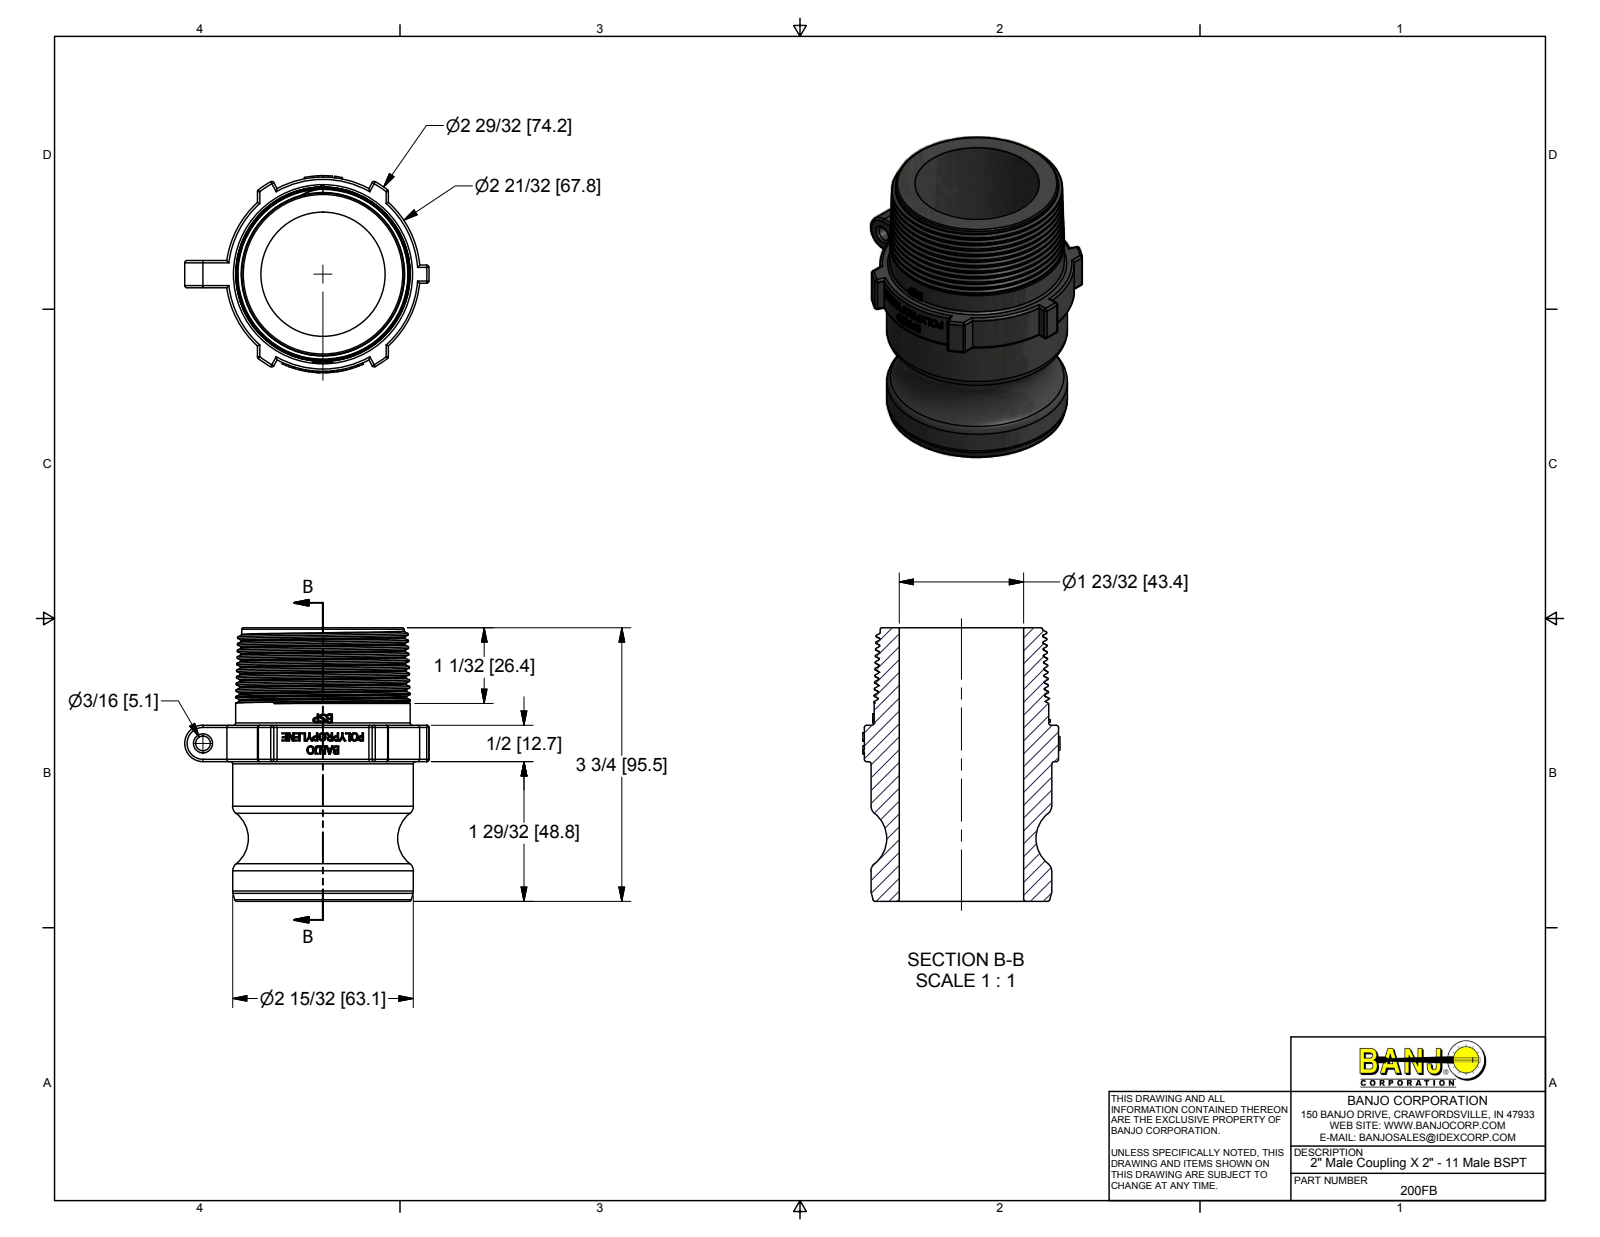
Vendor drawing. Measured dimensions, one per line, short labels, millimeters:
name: 200FB
written by: Autodesk Inventor 2014 (AUTOMOTIVE_DESIGN)
unit: mm
bodies: 1 solid, 539 faces (176 planar, 93 cylindrical, 270 other)
size: 95.5 × 85.34 × 68.83
volume: 139 565 mm³; area: 39 719 mm²
holes: 1× ⌀5.08, 1× ⌀43.43
bosses: 1× ⌀63.09, 1× ⌀60.96
rounds: 30× R0.79, 1× R6.35, 1× R30.99, 1× R33.91, 1× R34.42, 1× R37.08
face distances: 95.5, 34.03, 61.47, 46.73, 12.7, 48.77, 9.52, 45.72, 1.59, 7.93
